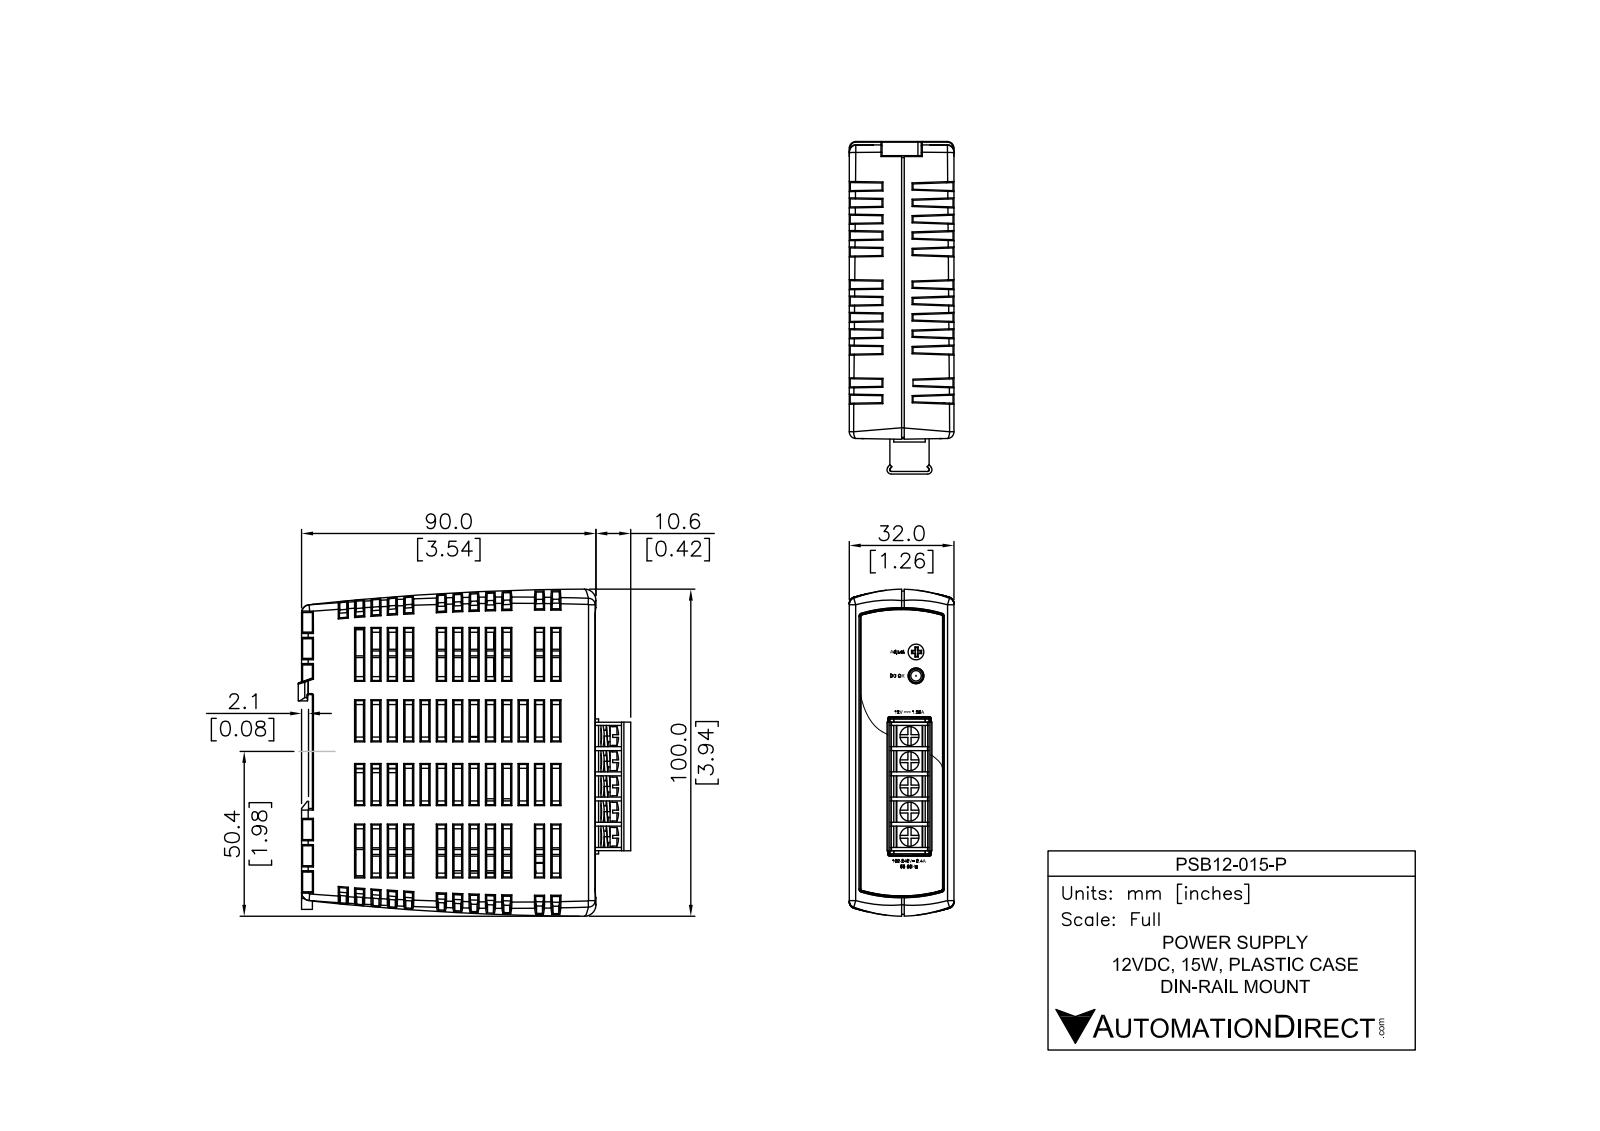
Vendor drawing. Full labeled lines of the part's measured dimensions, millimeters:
Part name (STEP PRODUCT): PSB12-015-P
STEP written by: SolidWorks 2011 (CONFIG_CONTROL_DESIGN)
Units: millimetres
Bodies: 1 solid, 1228 faces (965 planar, 55 cylindrical, 208 other)
Overall size (bounding box): 100.8 × 100.2 × 32
Volume: 191 600 mm³ · Surface area: 60 380 mm²
Round holes (diameter × count): ⌀4.4 ×2
Round bosses / shafts (diameter × count): ⌀5.1 ×5, ⌀2.4 ×1
Partial cylindrical surfaces — rounded edges, fillets, slot ends (radius × count): R0.4 ×10, R1.5 ×6, R0.8 ×2, R0.8 ×2, R44.5 ×1
Main face-to-face distances: 22.6, 9.4, 32, 2, 30, 7.4, 10.2, 20.3, 30.5, 5.1
Hole centre spacings: 7.6
